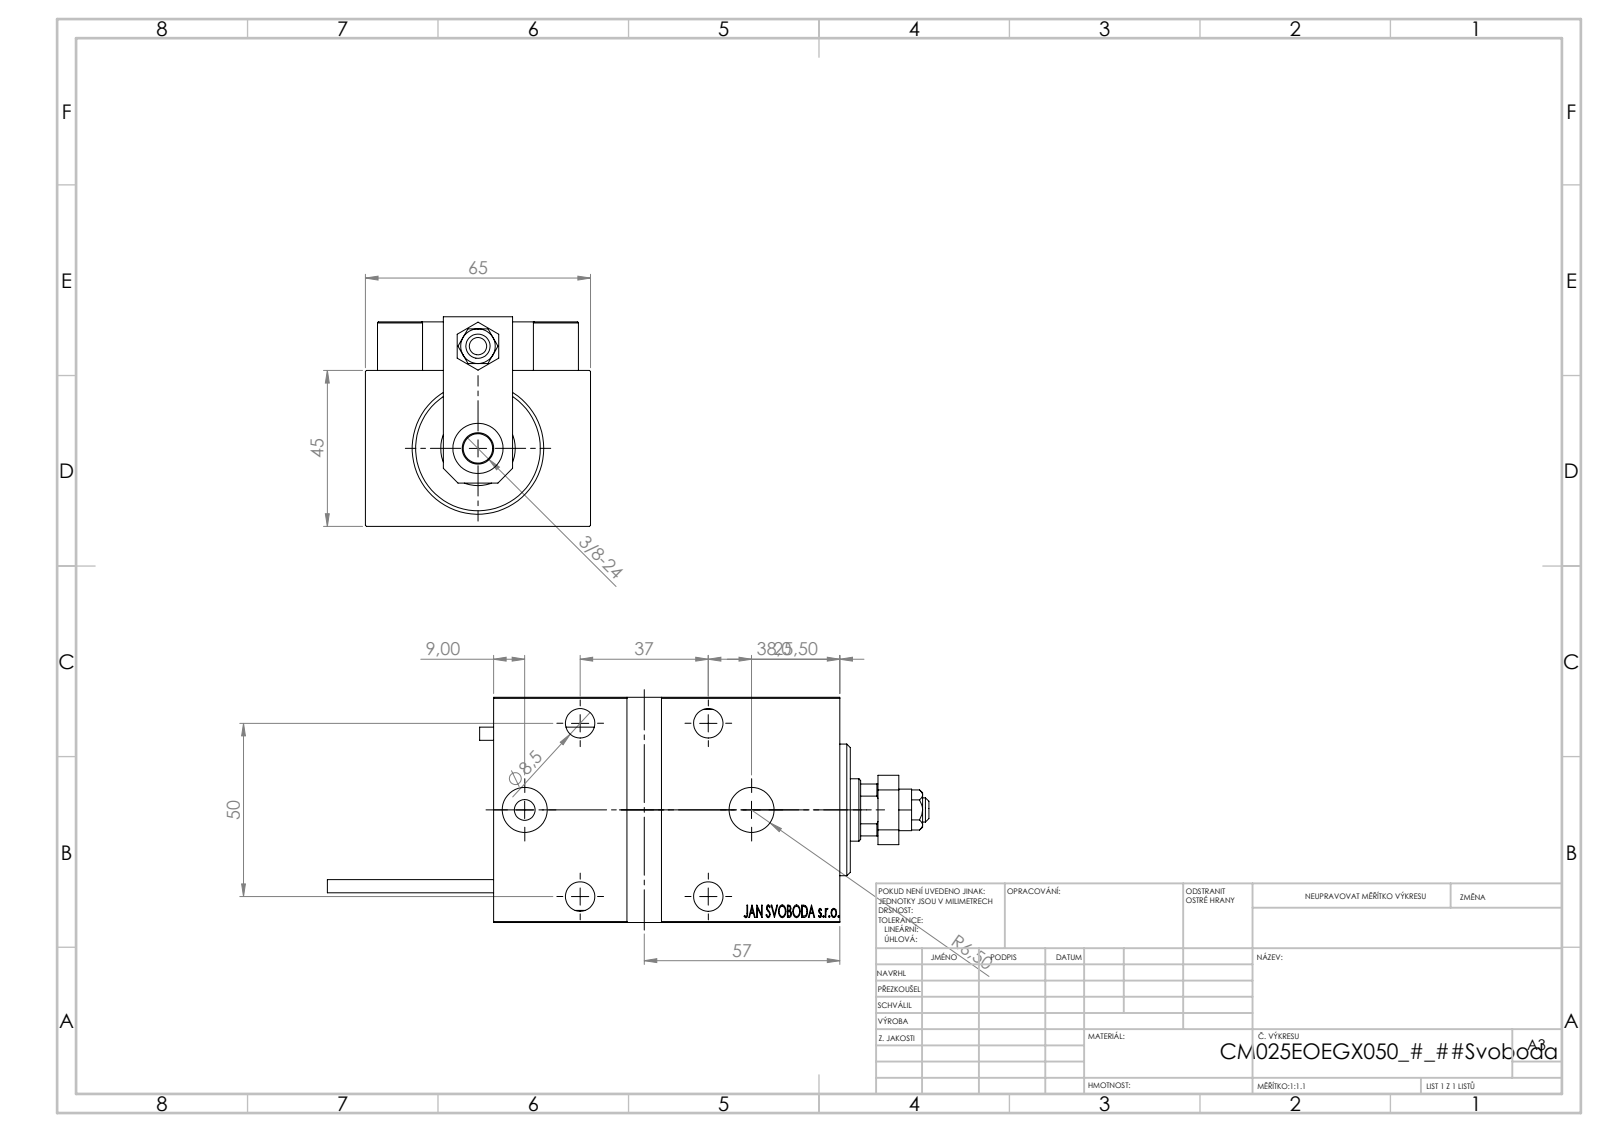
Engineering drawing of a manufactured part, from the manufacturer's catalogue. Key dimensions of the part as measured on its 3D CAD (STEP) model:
Part name (STEP PRODUCT): ALLEN BOLT D8; NUT_D12; Block; NUT_D10 (+8 more)
STEP written by: SolidWorks 2019 (CONFIG_CONTROL_DESIGN)
Units: millimetres
Bodies: 24 solids, 1286 faces (569 planar, 176 cylindrical, 541 other)
Overall size (bounding box): 173.7 × 65 × 60.5
Volume: 317 688 mm³ · Surface area: 77 608 mm²
Round holes (diameter × count): ⌀8 ×5, ⌀8.5 ×5, ⌀3.2 ×4, ⌀4 ×4, ⌀13.5 ×4, ⌀5 ×2, ⌀13 ×2, ⌀7 ×1, ⌀14.5 ×1, ⌀18 ×1, ⌀21.5 ×1, ⌀25 ×1
Round bosses / shafts (diameter × count): ⌀5 ×2, ⌀3.8 ×2, ⌀38 ×1, ⌀27 ×1, ⌀13 ×1, ⌀11 ×1, ⌀6 ×1
Partial cylindrical surfaces — rounded edges, fillets, slot ends (radius × count): R0.3 ×30, R3 ×2, R8.5 ×1
Main face-to-face distances: 45, 65, 14, 59, 6, 100, 13, 111, 10, 5
Hole centre spacings: 40.31, 10.77, 11.37, 20, 21.03, 25, 27.95, 29.59
